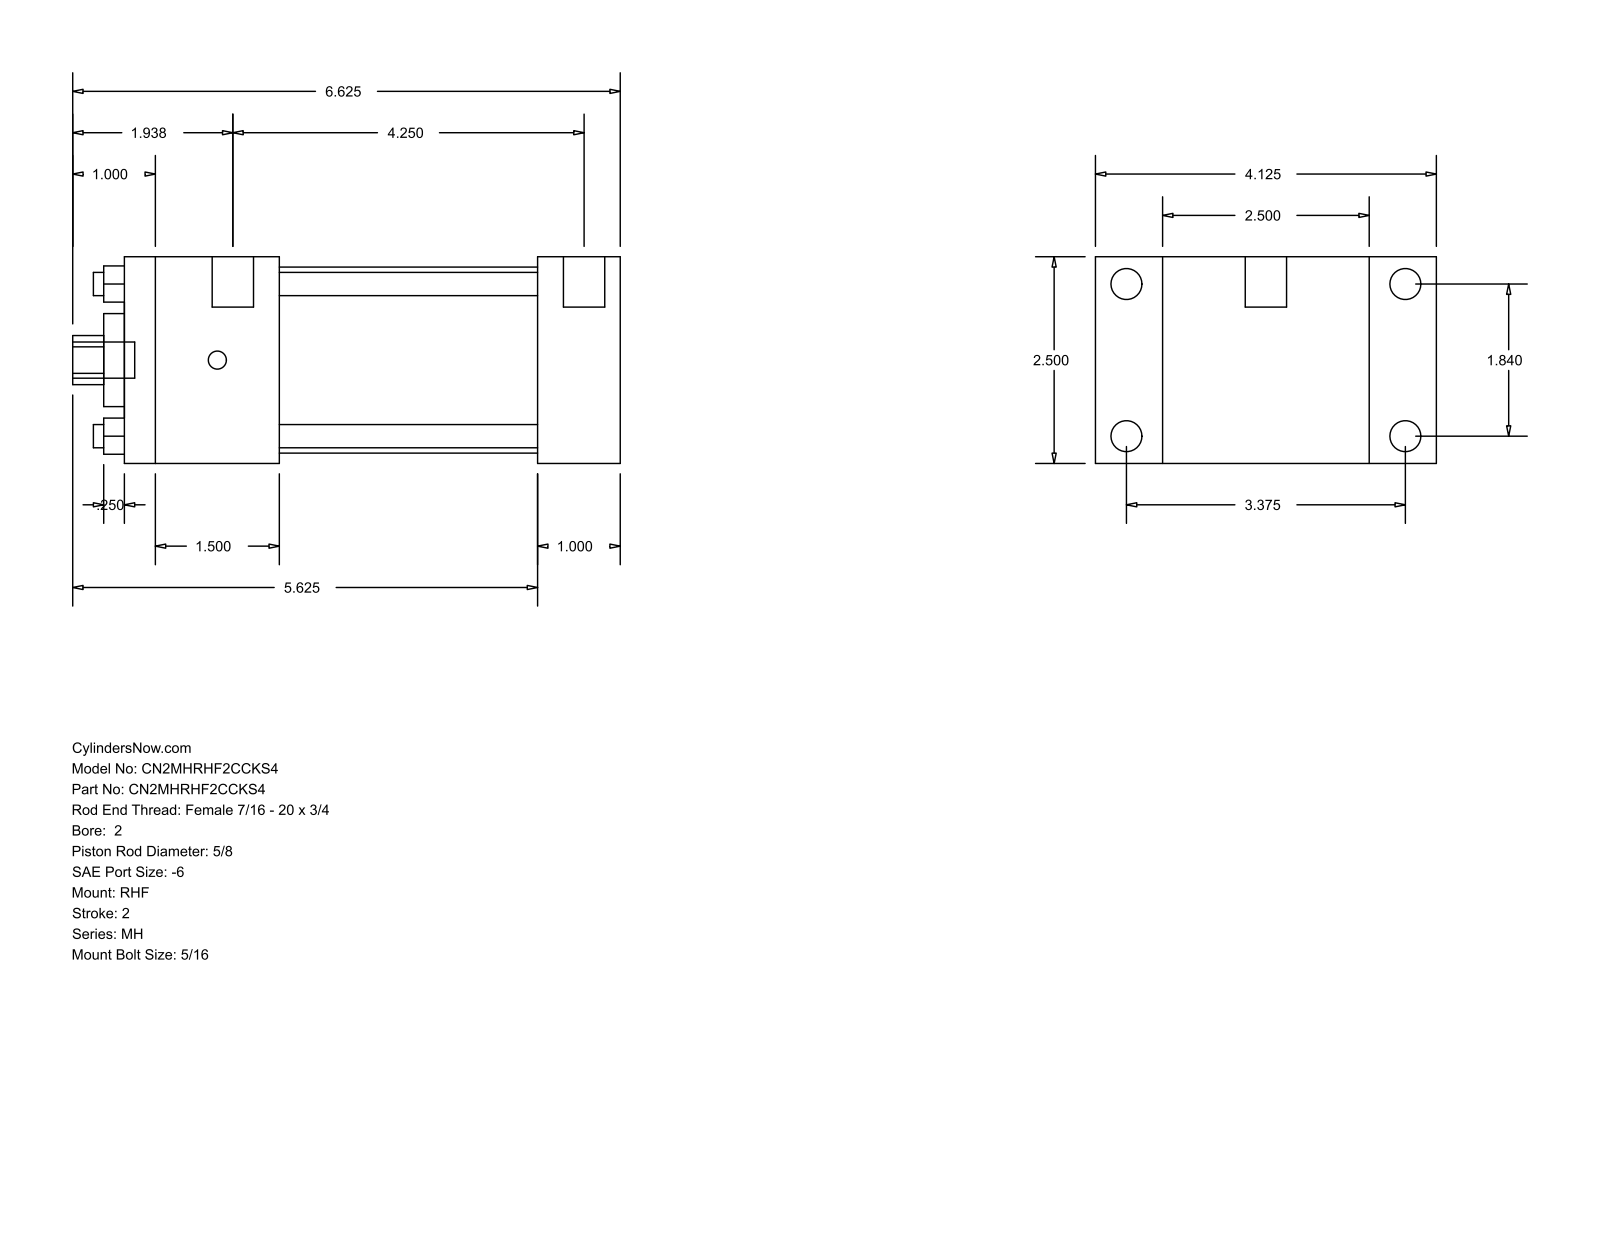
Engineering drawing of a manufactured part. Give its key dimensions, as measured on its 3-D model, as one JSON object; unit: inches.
{"part_name": "MH_RHF__0200_0.625", "step_written_by": "GSSL Pune (CONFIG_CONTROL_DESIGN)", "units": "inches", "bodies": {"solids": 0, "faces": 88, "planar": 60, "cylindrical": 28, "other": 0}, "overall_size": [6.625, 4.125, 2.5], "round_holes": [[0.281, 4], [0.625, 1], [1.125, 1], [2.25, 1]], "round_bosses_or_shafts": [[0.375, 4], [0.219, 4], [0.5, 2], [0.437, 1]], "partial_cylinders_radius": [[0.297, 1]], "face_to_face_distances": [2.5, 1, 0.813, 3.313, 5, 6, 4.125, 1.875, 3.125, 0.25], "hole_center_spacings": [1.301, 1.84, 2.602]}
